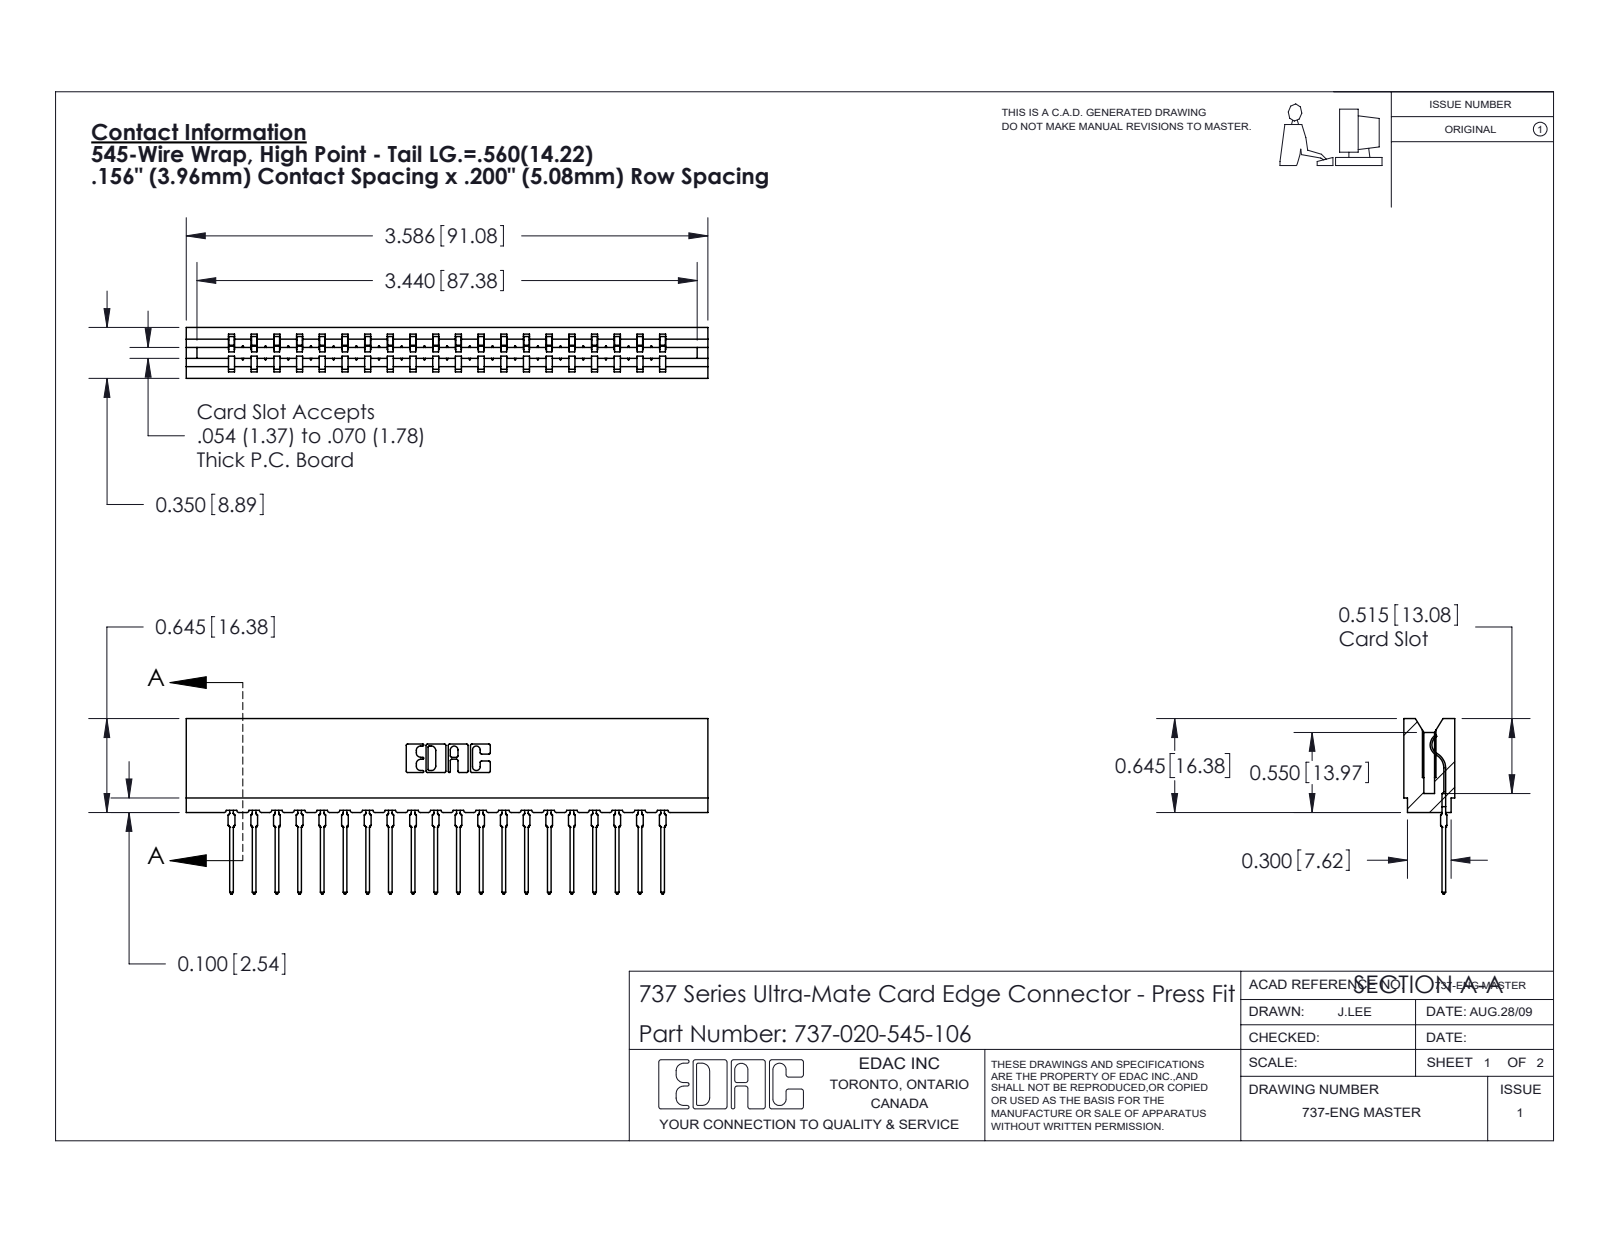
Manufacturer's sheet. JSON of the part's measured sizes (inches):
{"part_name": "737-020-545-106; 737 Part_Insulator Option - 06; 745-292-001_545", "step_written_by": "SolidWorks 2020 (CONFIG_CONTROL_DESIGN)", "units": "inches", "bodies": {"solids": 21, "faces": 2355, "planar": 1415, "cylindrical": 420, "other": 520}, "overall_size": [3.586, 1.206, 0.35], "volume_in3": 0.549, "surface_area_in2": 18.61, "partial_cylinders_radius": [[0.015, 40], [0.021, 40], [0.01, 22], [0.007, 6], [0.031, 6], [0.005, 4], [0.011, 4], [0.026, 3]], "face_to_face_distances": [0.138, 0.212, 0.35, 0.156, 0.624, 0.468, 0.78, 0.074, 0.045, 0.305]}
